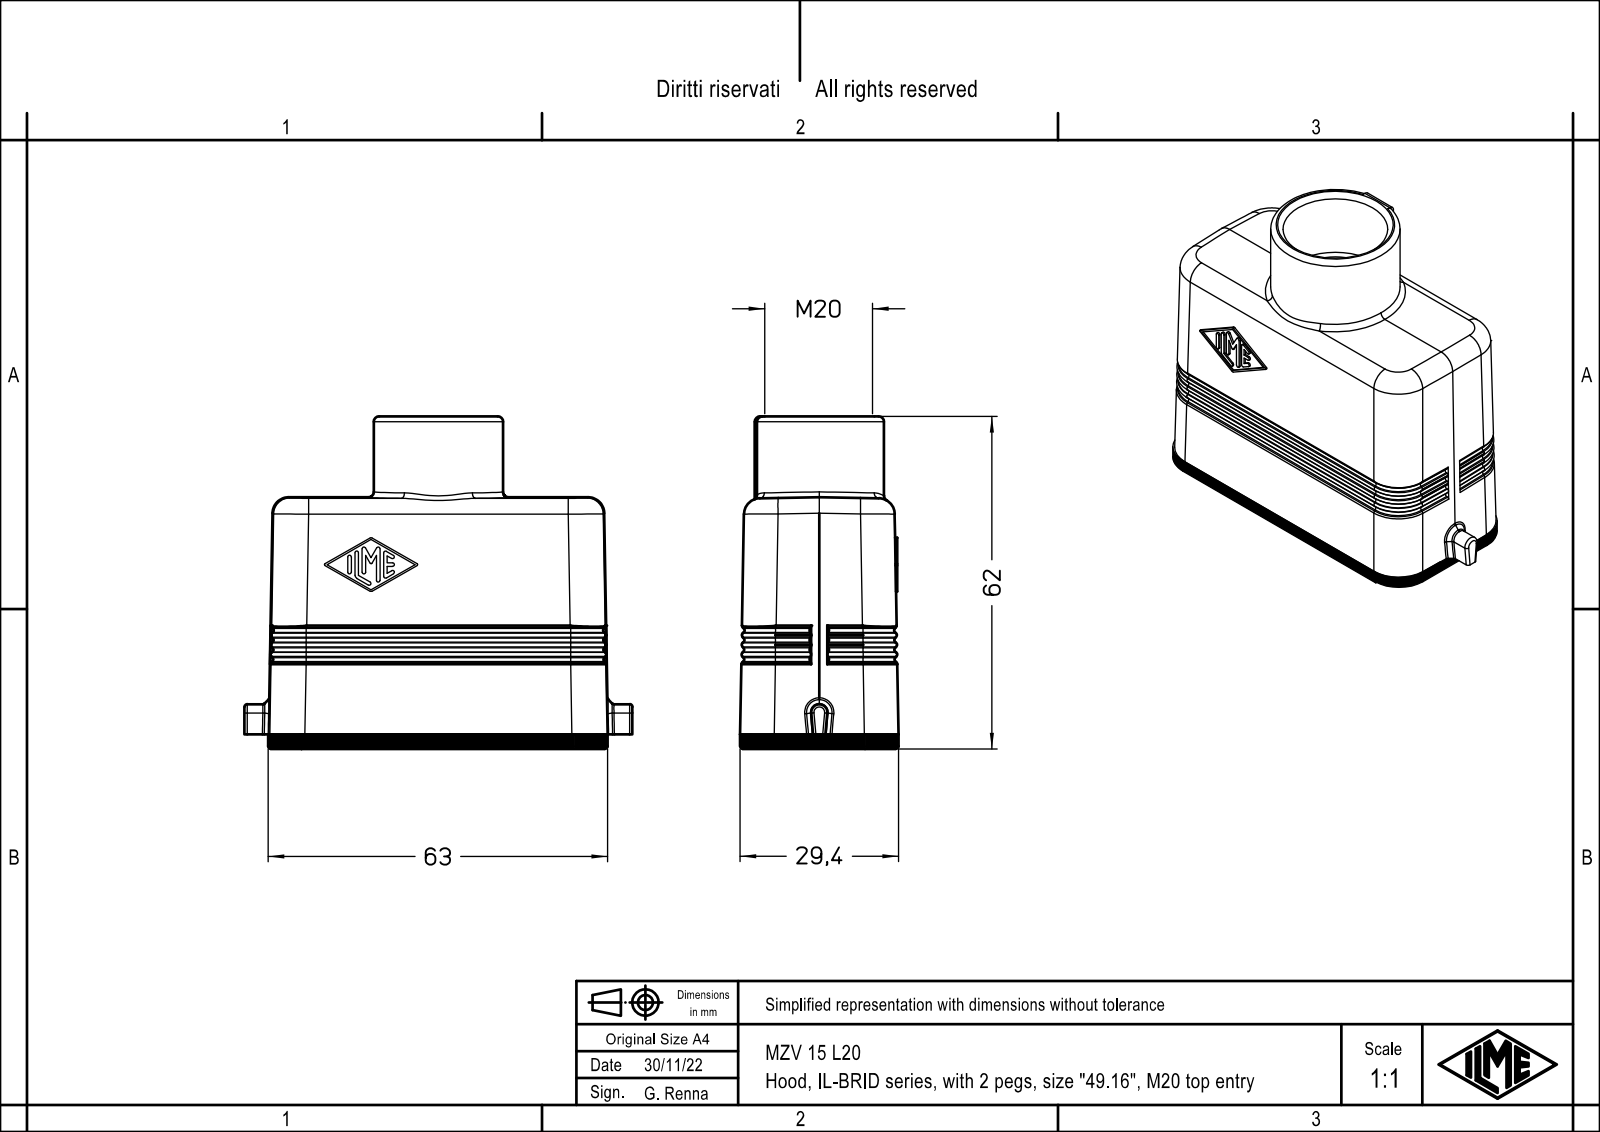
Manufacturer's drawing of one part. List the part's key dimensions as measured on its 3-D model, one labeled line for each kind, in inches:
Part name (STEP PRODUCT): CZ_MZ Tüllengehäuse 1 Bügel
STEP written by: Autodesk Inventor 7 (AUTOMOTIVE_DESIGN)
Units: inches
Bodies: 1 solid, 322 faces (153 planar, 86 cylindrical, 83 other)
Overall size (bounding box): 2.835 × 2.441 × 1.158
Volume: 2.175 in³ · Surface area: 33.01 in²
Round holes (diameter × count): ⌀0.097 ×4, ⌀0.138 ×4, ⌀0.709 ×1, ⌀0.787 ×1
Round bosses / shafts (diameter × count): ⌀0.945 ×1, ⌀0.142 ×1
Partial cylindrical surfaces — rounded edges, fillets, slot ends (radius × count): R0.01 ×14, R0.079 ×8, R0.157 ×8, R0.049 ×4, R0.13 ×2
Main face-to-face distances: 0.118, 1.039, 1.157, 0.921, 0.394, 2.087, 2.362, 1.969, 0.044, 2.48
Hole centre spacings: 1.024, 0.63, 1.949, 2.048
